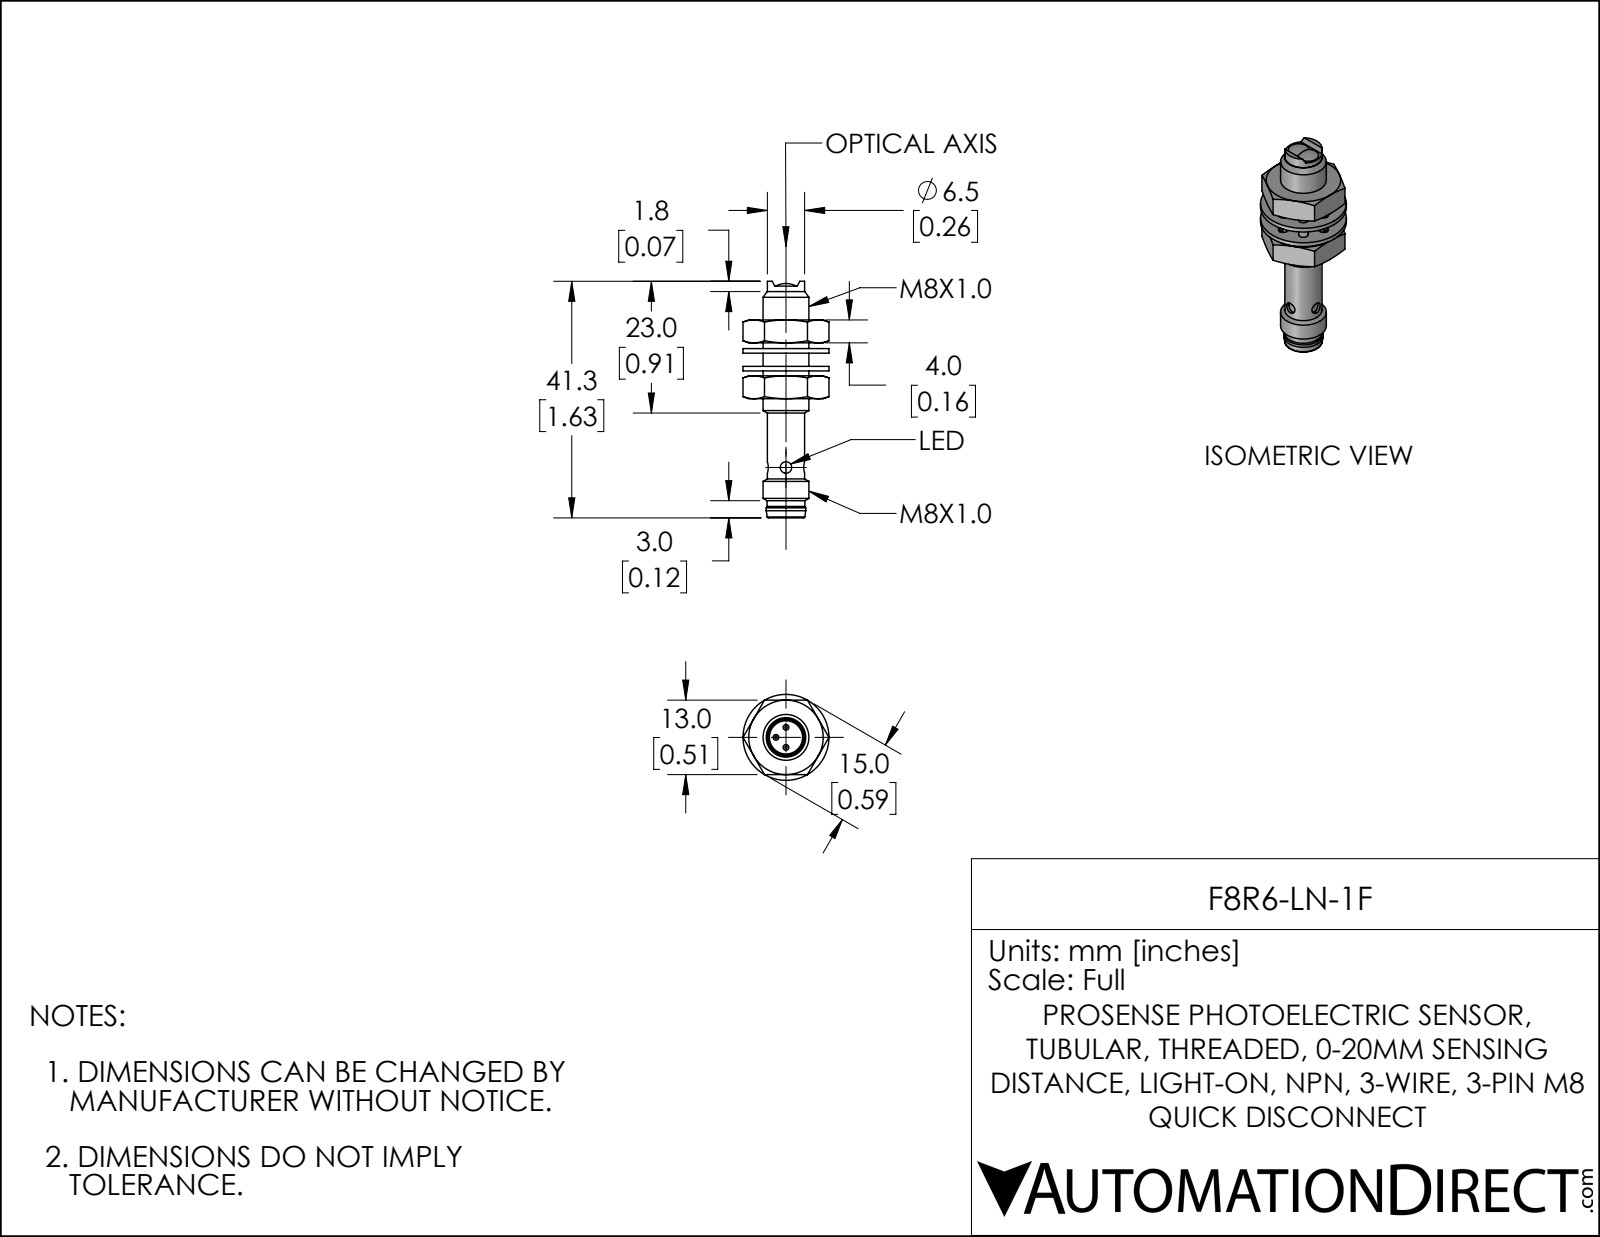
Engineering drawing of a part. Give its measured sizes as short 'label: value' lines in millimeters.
name: F8R6-LN-1F
written by: SolidWorks 2019 (CONFIG_CONTROL_DESIGN)
unit: mm
bodies: 5 solids, 157 faces (63 planar, 54 cylindrical, 40 other)
size: 41.3 × 15 × 15
volume: 2 650 mm³; area: 2 690 mm²
holes: 2× ⌀2, 1× ⌀5.8, 1× ⌀6.9
bosses: 3× ⌀1, 1× ⌀15, 1× ⌀8, 1× ⌀6.9, 1× ⌀6.6, 1× ⌀6.5
rounds: 8× R0.8, 1× R2.8, 1× R4.2
face distances: 3.1, 0.8, 13, 9.8, 4, 3.9, 2.3, 0.8, 1.7, 5
